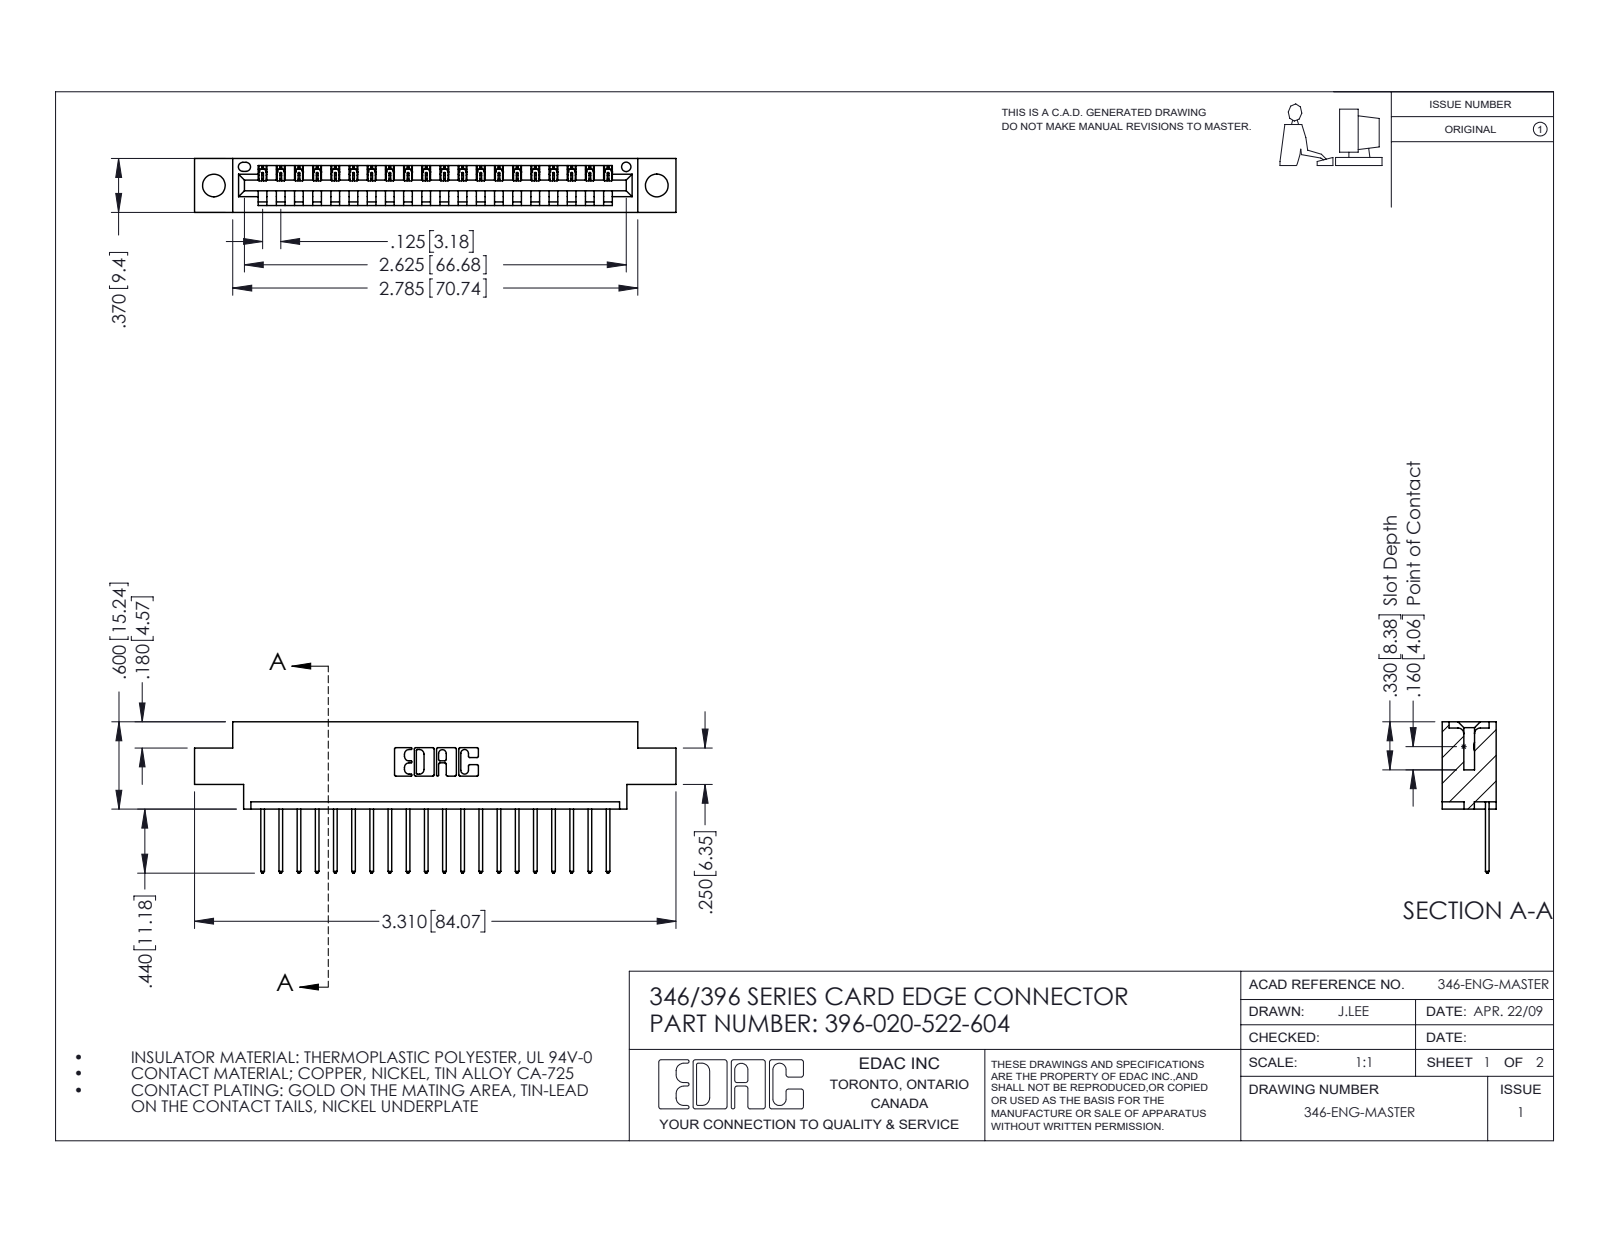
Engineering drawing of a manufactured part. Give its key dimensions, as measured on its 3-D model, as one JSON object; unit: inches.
{"part_name": "345-292-001_345-293-122; 346 Part_0.170 Offset - 0.156 Dia-TH; 396-020-522-604", "step_written_by": "SolidWorks 2016 (CONFIG_CONTROL_DESIGN)", "units": "inches", "bodies": {"solids": 21, "faces": 1286, "planar": 880, "cylindrical": 406, "other": 0}, "overall_size": [3.31, 1.04, 0.37], "volume_in3": 0.467, "surface_area_in2": 14.52, "round_holes": [[0.156, 2], [0.064, 1]], "partial_cylinders_radius": [[0.006, 40], [0.01, 40], [0.01, 22], [0.007, 6], [0.031, 6], [0.026, 3], [0.031, 2], [0.04, 2]], "face_to_face_distances": [0.048, 0.322, 0.37, 0.25, 0.072, 0.298, 0.025, 0.148, 0.222, 0.1], "hole_center_spacings": [0.246, 2.837, 3.045]}
